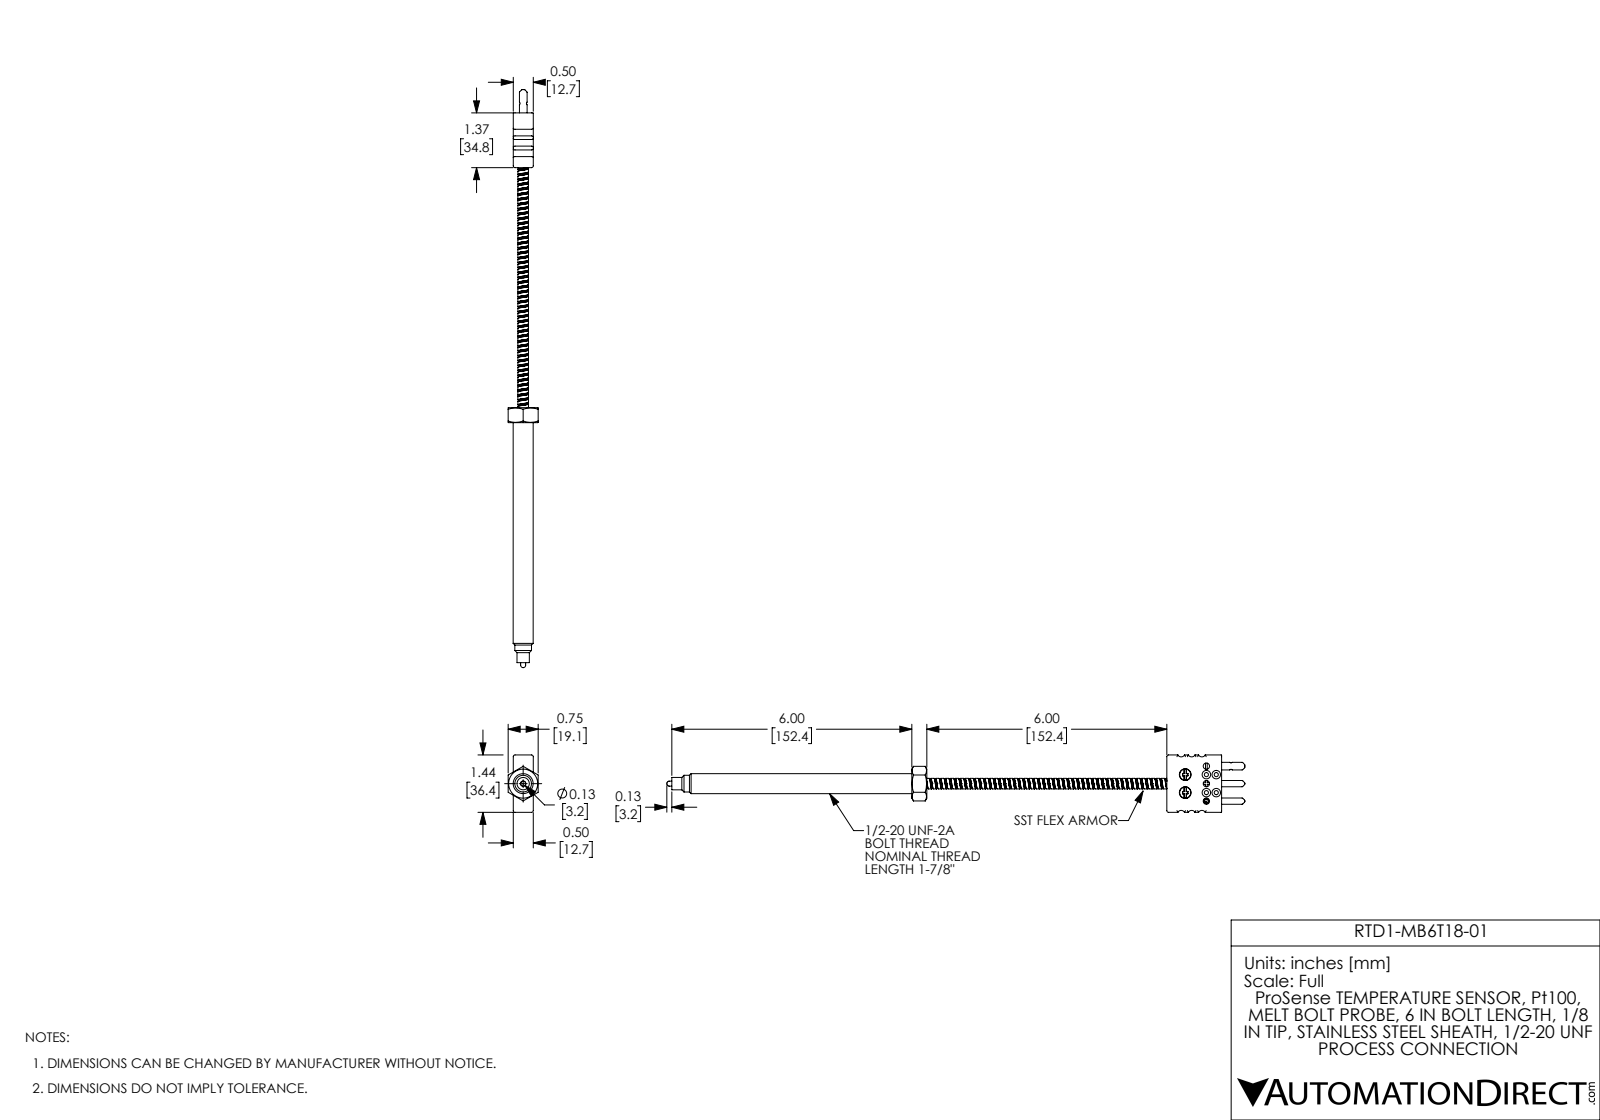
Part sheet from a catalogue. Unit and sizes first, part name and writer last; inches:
Units: inches
Overall size (bounding box): 14.451 × 1.435 × 0.75
Round holes (diameter × count): ⌀0.103 ×4, ⌀0.158 ×3, ⌀0.185 ×2, ⌀0.294 ×2, ⌀0.135 ×1, ⌀0.308 ×1
Round bosses / shafts (diameter × count): ⌀0.278 ×2, ⌀0.156 ×2, ⌀0.102 ×2, ⌀0.5 ×1, ⌀0.417 ×1, ⌀0.309 ×1, ⌀0.265 ×1, ⌀0.191 ×1
Partial cylindrical surfaces — rounded edges, fillets, slot ends (radius × count): R0.045 ×8, R0.095 ×6, R0.01 ×4
Main face-to-face distances: 0.5, 6, 1.369, 0.75, 7.369, 1.435, 6.375, 7.744, 0.375, 0.622
Hole centre spacings: 0.529, 0.57, 0.776, 0.212, 0.225, 0.247, 0.326, 0.334
Volume: 2.569 in³ · Surface area: 26.51 in²
Bodies: 3 solids, 412 faces (106 planar, 190 cylindrical, 116 other)
Part name (STEP PRODUCT): RTD1-MB6T18-01
STEP written by: SolidWorks 2017 (AUTOMOTIVE_DESIGN)
